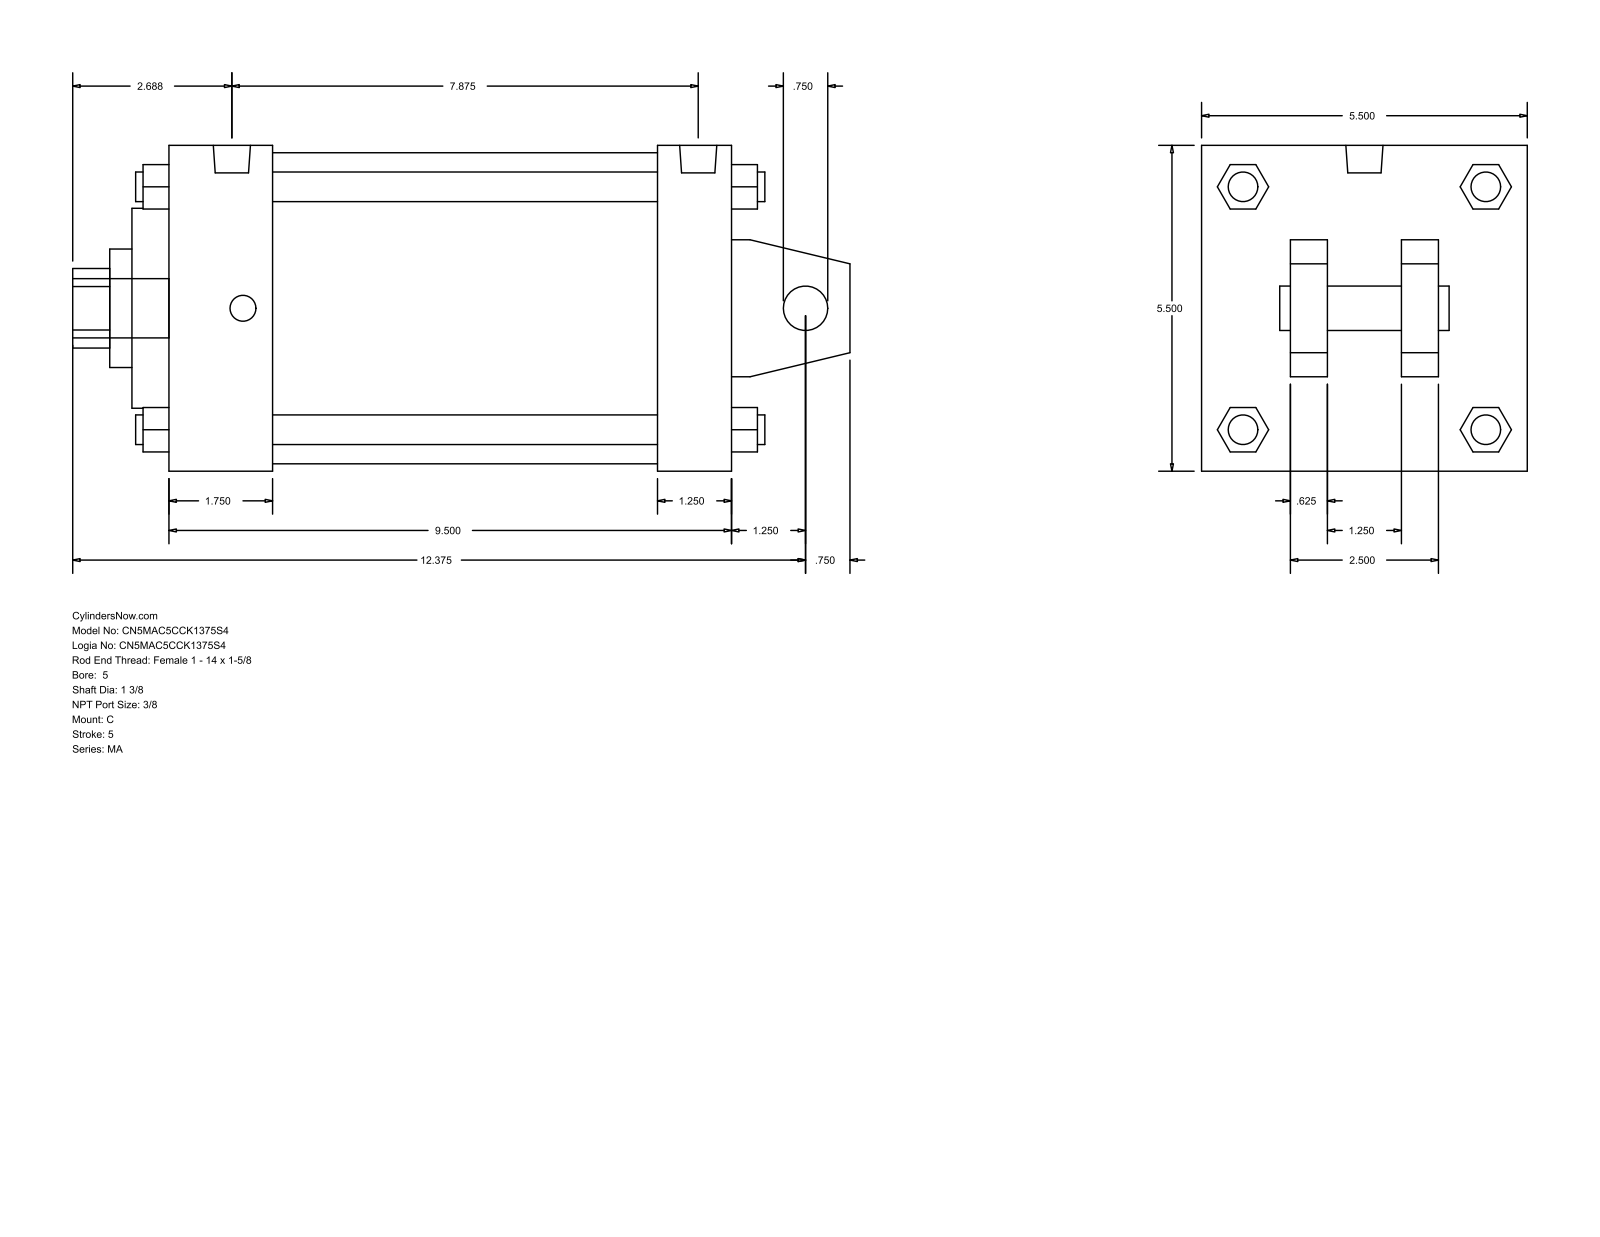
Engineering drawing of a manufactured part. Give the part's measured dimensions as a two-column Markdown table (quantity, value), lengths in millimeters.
| quantity | value |
| --- | --- |
| part name | MA_C__0500_1.375 |
| STEP written by | GSSL Pune (CONFIG_CONTROL_DESIGN) |
| units | millimeters |
| bodies | 0 solids, 141 faces (109 planar, 32 cylindrical, 0 other) |
| overall size | 333.38 × 139.7 × 139.7 |
| round holes (diameter × count) | 19.05 × 1, 34.92 × 1, 50.8 × 1, 85.72 × 1, 133.35 × 1 |
| round bosses / shafts (diameter × count) | 12.7 × 4, 11.11 × 4, 15.93 × 2, 25.4 × 1 |
| partial cylindrical surfaces (radius × count) | 17.06 × 1 |
| main face-to-face distances | 139.7, 241.3, 15.87, 209.55, 31.75, 44.45, 165.1, 196.85, 38.1, 101.6 |
